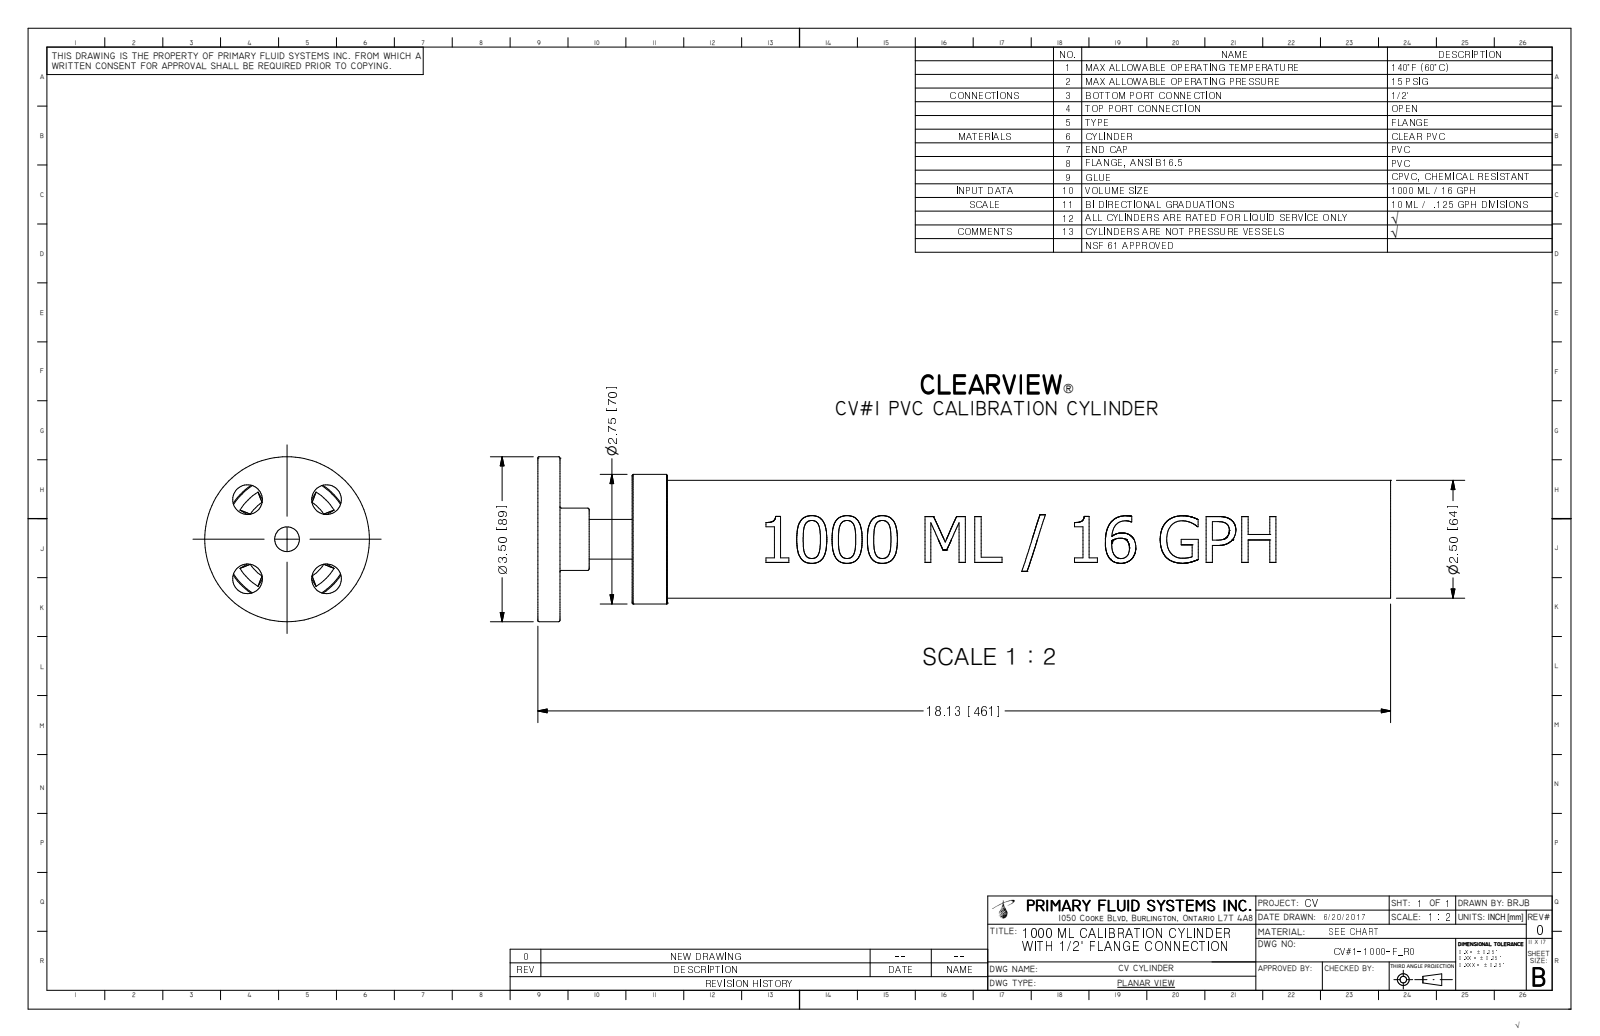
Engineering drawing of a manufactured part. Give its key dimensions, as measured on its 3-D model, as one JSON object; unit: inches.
{"part_name": "PV#1-1000-F_R0", "step_written_by": "Autodesk Inventor 2009 (AUTOMOTIVE_DESIGN)", "units": "inches", "bodies": {"solids": 2, "faces": 254, "planar": 90, "cylindrical": 30, "other": 134}, "overall_size": [18.13, 3.5, 3.5], "volume_in3": 15.37, "surface_area_in2": 307.2, "round_holes": [[0.63, 4], [0.526, 1], [0.719, 1], [2.38, 1], [2.52, 1]], "round_bosses_or_shafts": [[3.5, 1], [2.75, 1], [2.5, 1], [2.36, 1], [1.32, 1]], "partial_cylinders_radius": [[1.249, 1]], "face_to_face_distances": [0.47, 2.005, 1.535, 2.755, 2.285, 0.75, 2.38, 1.91, 0.375, 0.375], "hole_center_spacings": [1.188, 1.68, 2.375]}
